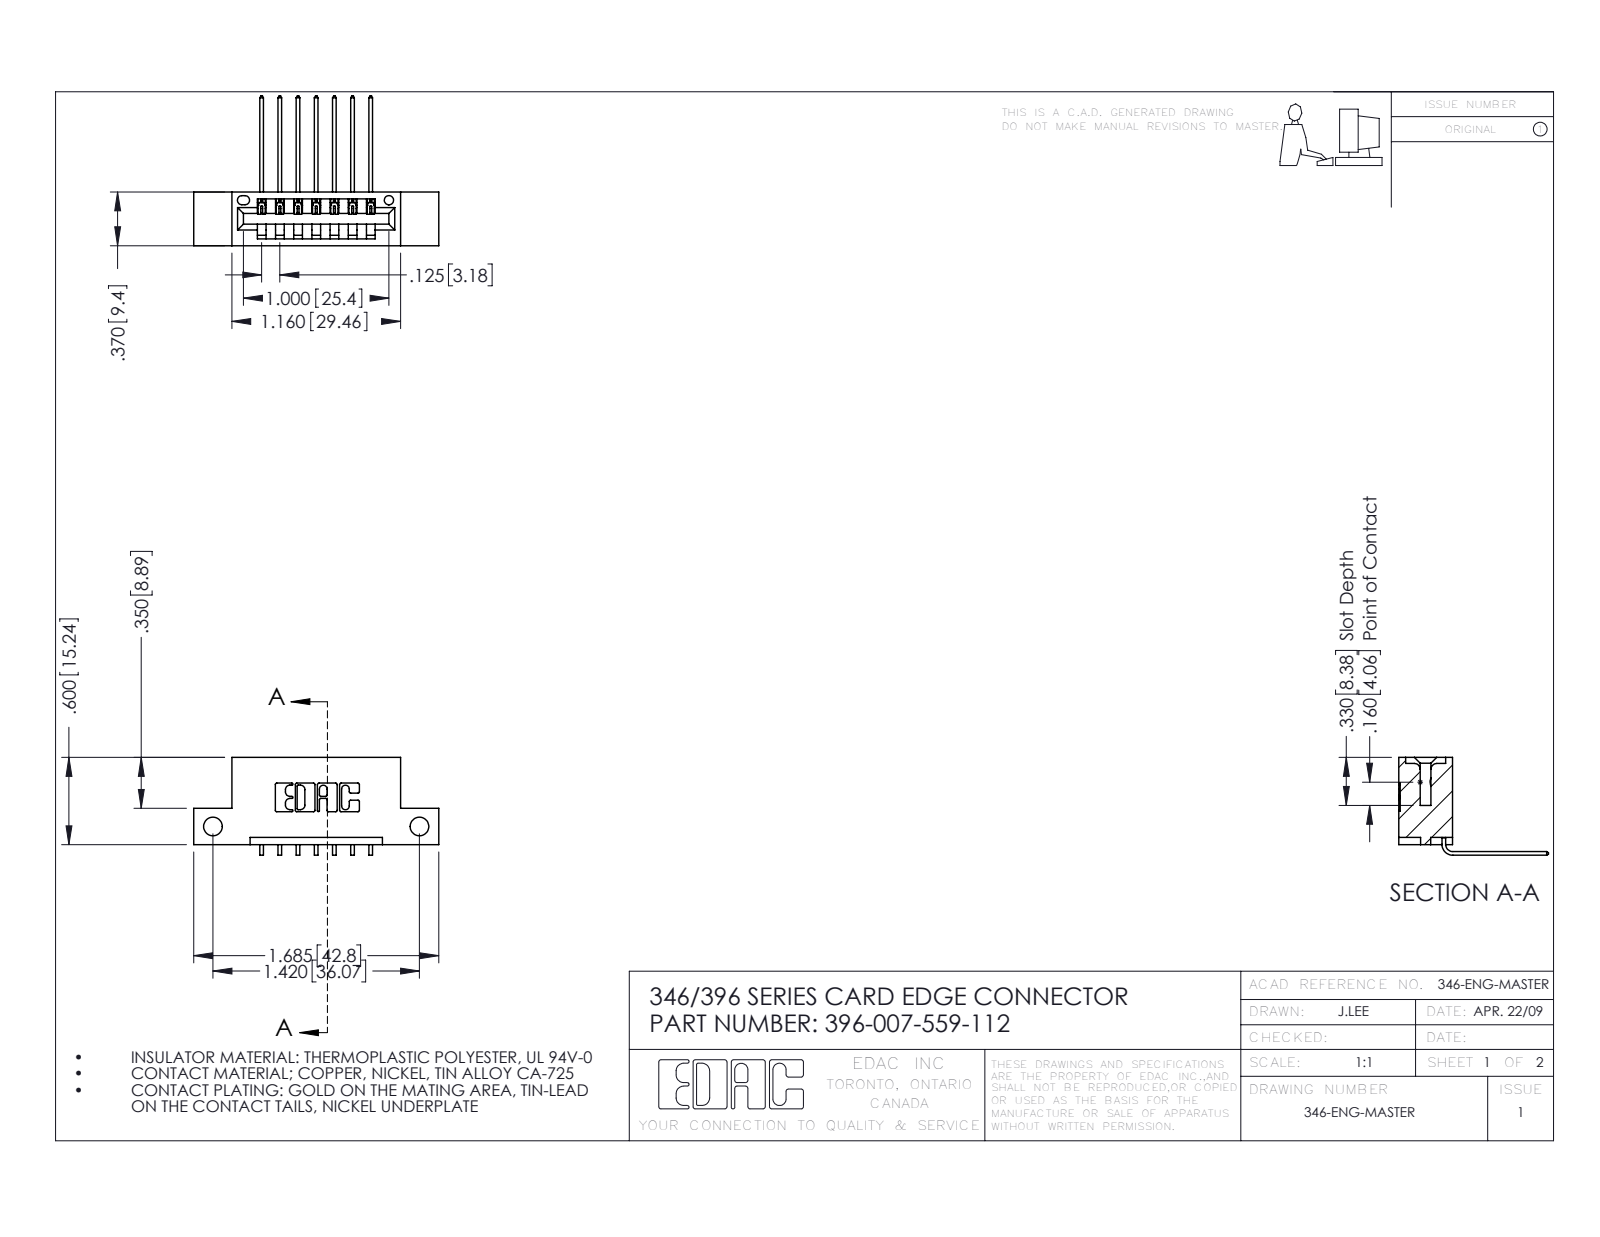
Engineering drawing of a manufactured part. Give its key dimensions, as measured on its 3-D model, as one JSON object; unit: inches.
{"part_name": "346 Part_Flush Mounting Lugs - Side Mount; 396-007-559-112; 345-292-001_558 559 Tail - 1", "step_written_by": "SolidWorks 2016 (CONFIG_CONTROL_DESIGN)", "units": "inches", "bodies": {"solids": 8, "faces": 542, "planar": 370, "cylindrical": 172, "other": 0}, "overall_size": [1.685, 1.03, 0.673], "volume_in3": 0.231, "surface_area_in2": 6.75, "round_holes": [[0.128, 2], [0.064, 1]], "partial_cylinders_radius": [[0.01, 22], [0.006, 14], [0.007, 6], [0.031, 6], [0.026, 3], [0.031, 2], [0.04, 2], [0.014, 1]], "face_to_face_distances": [0.25, 0.048, 0.322, 0.37, 0.072, 0.298, 0.025, 0.148, 0.222, 0.1], "hole_center_spacings": [1.42]}
